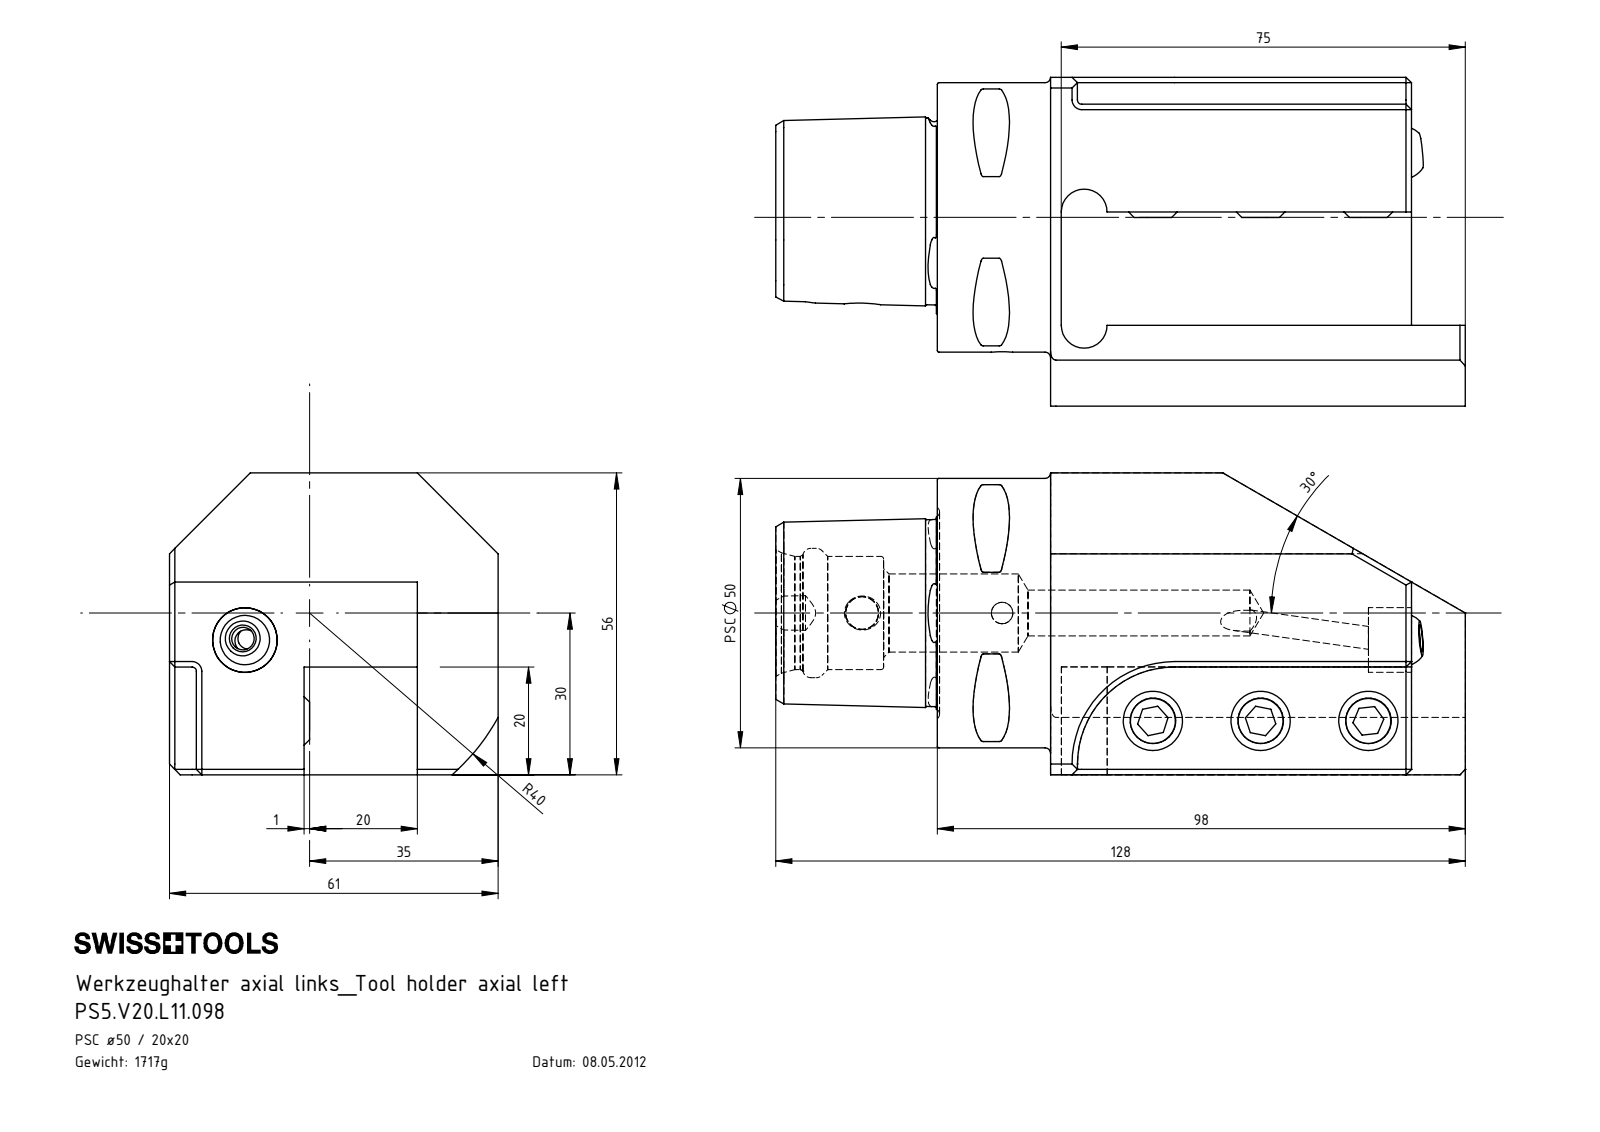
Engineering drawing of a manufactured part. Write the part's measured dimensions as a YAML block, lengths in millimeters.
part_name: "KU1-U12.001.010_1; ISO 4026 - M10 x 20; PS5-V20.L11.098_A; KU1-U12.001.010 (+2 more)"
step_written_by: "SolidWorks 2017 (AUTOMOTIVE_DESIGN)"
units: millimeters
bodies: {solids: 6, faces: 181, planar: 79, cylindrical: 35, other: 67}
overall_size: [128, 61, 56]
volume: 218551
surface_area: 38479
round_holes:
  - {diameter: 8.5, count: 4}
  - {diameter: 4.2, count: 2}
  - {diameter: 4, count: 1}
  - {diameter: 6.1, count: 1}
  - {diameter: 7, count: 1}
  - {diameter: 12, count: 1}
  - {diameter: 14.5, count: 1}
  - {diameter: 21, count: 1}
  - {diameter: 24, count: 1}
round_bosses_or_shafts:
  - {diameter: 10, count: 3}
  - {diameter: 50, count: 1}
partial_cylinders:
  - {radius: 0.5, count: 8}
  - {radius: 0.8, count: 2}
  - {radius: 5, count: 2}
  - {radius: 4, count: 1}
  - {radius: 18, count: 1}
  - {radius: 40, count: 1}
face_to_face_distances: [20, 36, 21, 56, 61, 15, 46, 67, 25, 5]
hole_center_spacings: [20, 13, 26, 34.41, 40, 52, 57.58, 70.88]
